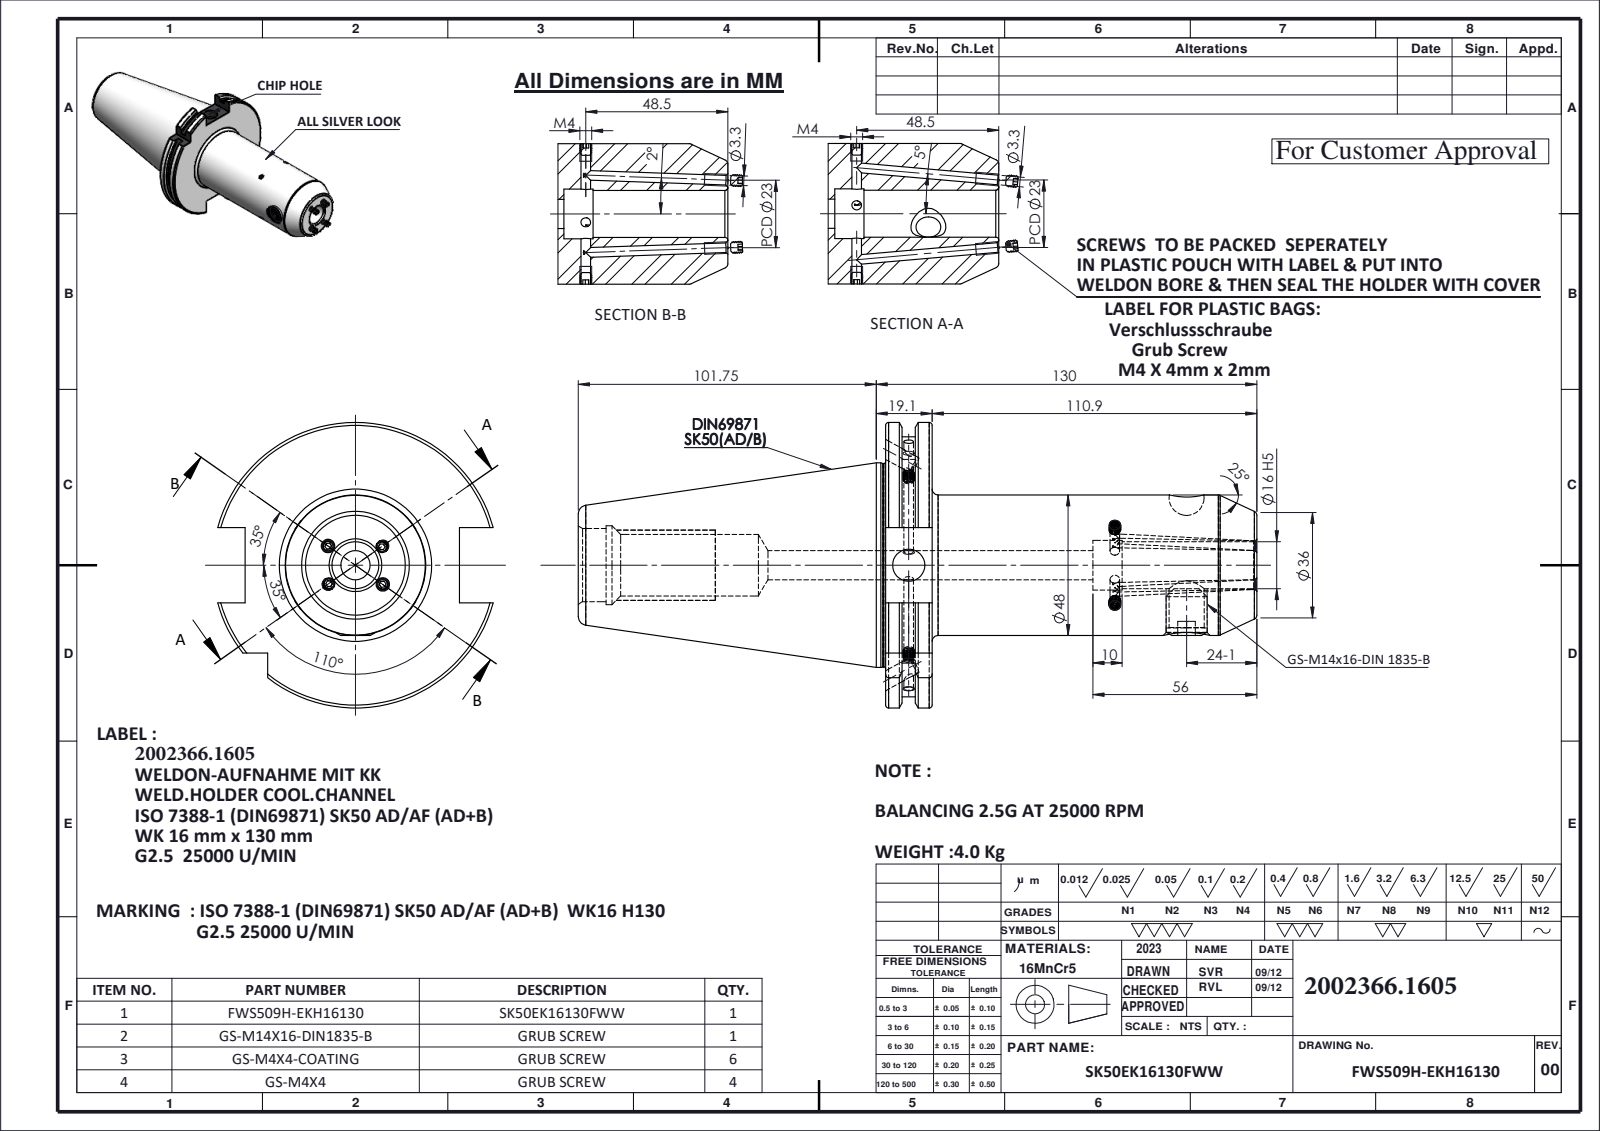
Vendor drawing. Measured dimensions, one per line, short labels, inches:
name: SK50EK16130FWW; GS-M4X4-COATING_DIN 913 - M4 x 4-N; FWS509H-EKH16130; GS-M4X4_DIN 913 - M4 x 4-N (+1 more)
written by: SolidWorks 2023 (CONFIG_CONTROL_DESIGN)
unit: in
bodies: 12 solids, 648 faces (125 planar, 179 cylindrical, 344 other)
size: 9.384 × 3.839 × 3.703
volume: 31.15 in³; area: 106.4 in²
holes: 9× ⌀0.13, 2× ⌀0.236, 1× ⌀0.394, 1× ⌀0.433, 1× ⌀0.472, 1× ⌀0.551, 1× ⌀0.63, 1× ⌀0.669, 1× ⌀0.827, 1× ⌀0.984, 1× ⌀1.063
bosses: 10× ⌀0.157, 1× ⌀2.75, 1× ⌀2.734, 1× ⌀1.89
rounds: 1× R1.768, 1× R1.919
face distances: 0.626, 4.992, 4.366, 0.223, 0.403, 4.769, 0.399, 0.176, 0.227, 4.593
